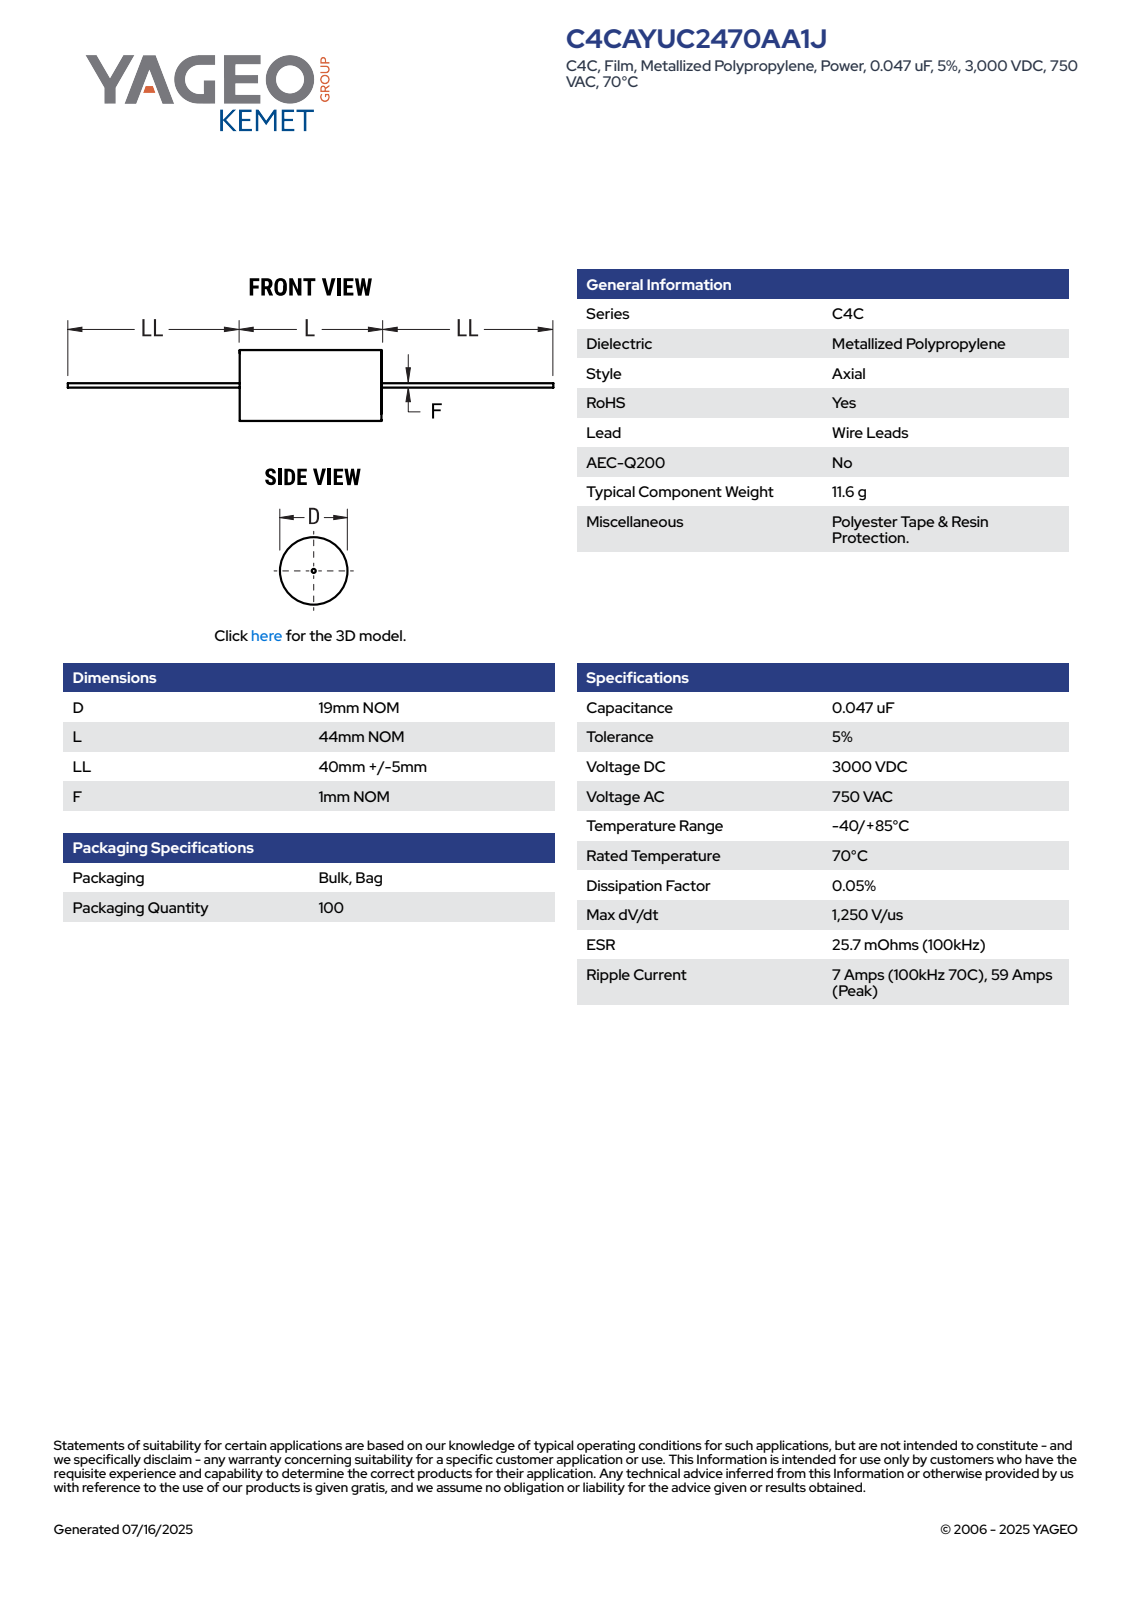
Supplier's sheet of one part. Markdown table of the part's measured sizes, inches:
| quantity | value |
| --- | --- |
| part name | CFP_ACWF_19X44_D19L44LL45F1 |
| STEP written by | SolidWorks 2014 (AUTOMOTIVE_DESIGN) |
| units | inches |
| bodies | 2 solids, 87 faces (28 planar, 28 cylindrical, 31 other) |
| overall size | 5.276 × 0.748 × 0.748 |
| volume | 0.766 in³ |
| surface area | 6.267 in² |
| round bosses / shafts (diameter × count) | 0.748 × 1, 0.039 × 1 |
| partial cylindrical surfaces (radius × count) | 0.374 × 1 |
| main face-to-face distances | 1.732, 1.732, 1.771, 1.772, 3.504, 5.276, 3.504, 3.504, 1.772 |
